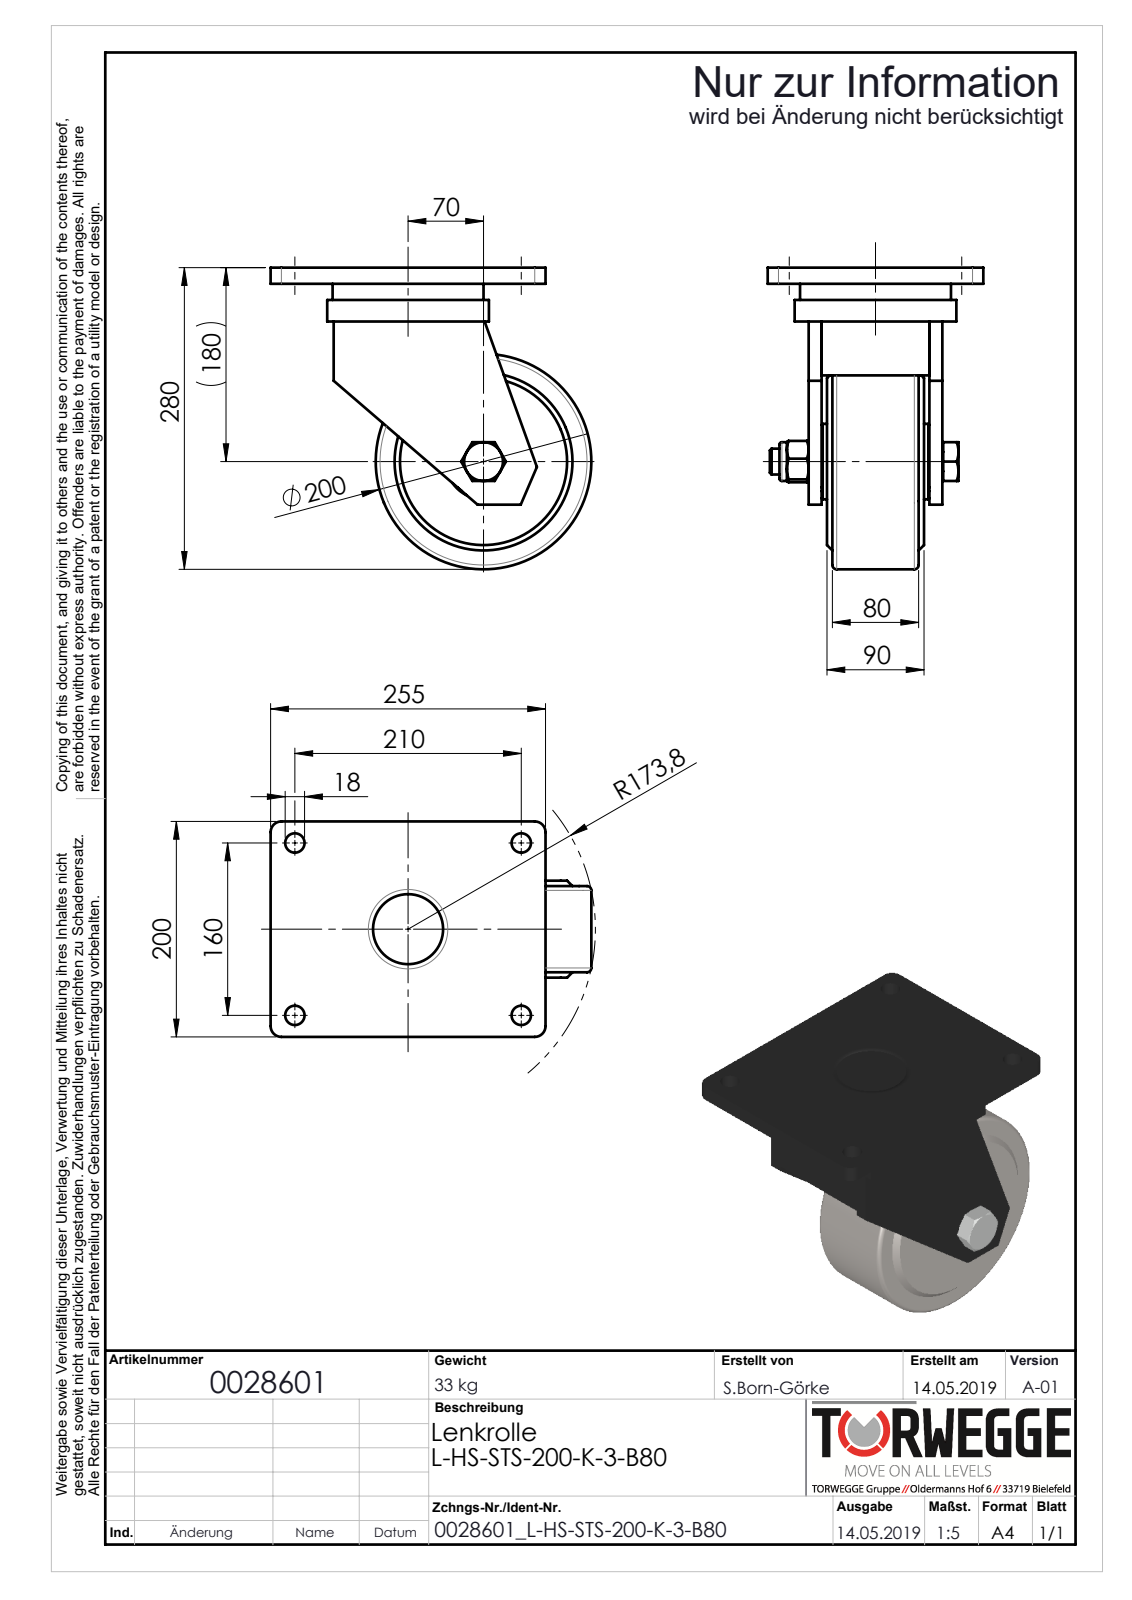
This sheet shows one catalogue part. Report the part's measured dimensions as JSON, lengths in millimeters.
{"part_name": "0028601_L-HS-STS-200-K-3-B80_(A-01)", "step_written_by": "SolidWorks 2018 (AUTOMOTIVE_DESIGN)", "units": "millimeters", "bodies": {"solids": 6, "faces": 151, "planar": 69, "cylindrical": 38, "other": 44}, "overall_size": [297.5, 280, 200], "volume_mm3": 4799000, "surface_area_mm2": 402844, "round_holes": [[18, 4], [21, 1], [24, 1], [24.2, 1], [25, 1], [27.43, 1]], "round_bosses_or_shafts": [[200, 1], [140, 1], [70, 1], [36, 1]], "partial_cylinders_radius": [[10, 4]], "face_to_face_distances": [12, 5, 15, 112, 17, 90, 107, 95, 50, 35], "hole_center_spacings": [160, 210, 264.01]}
